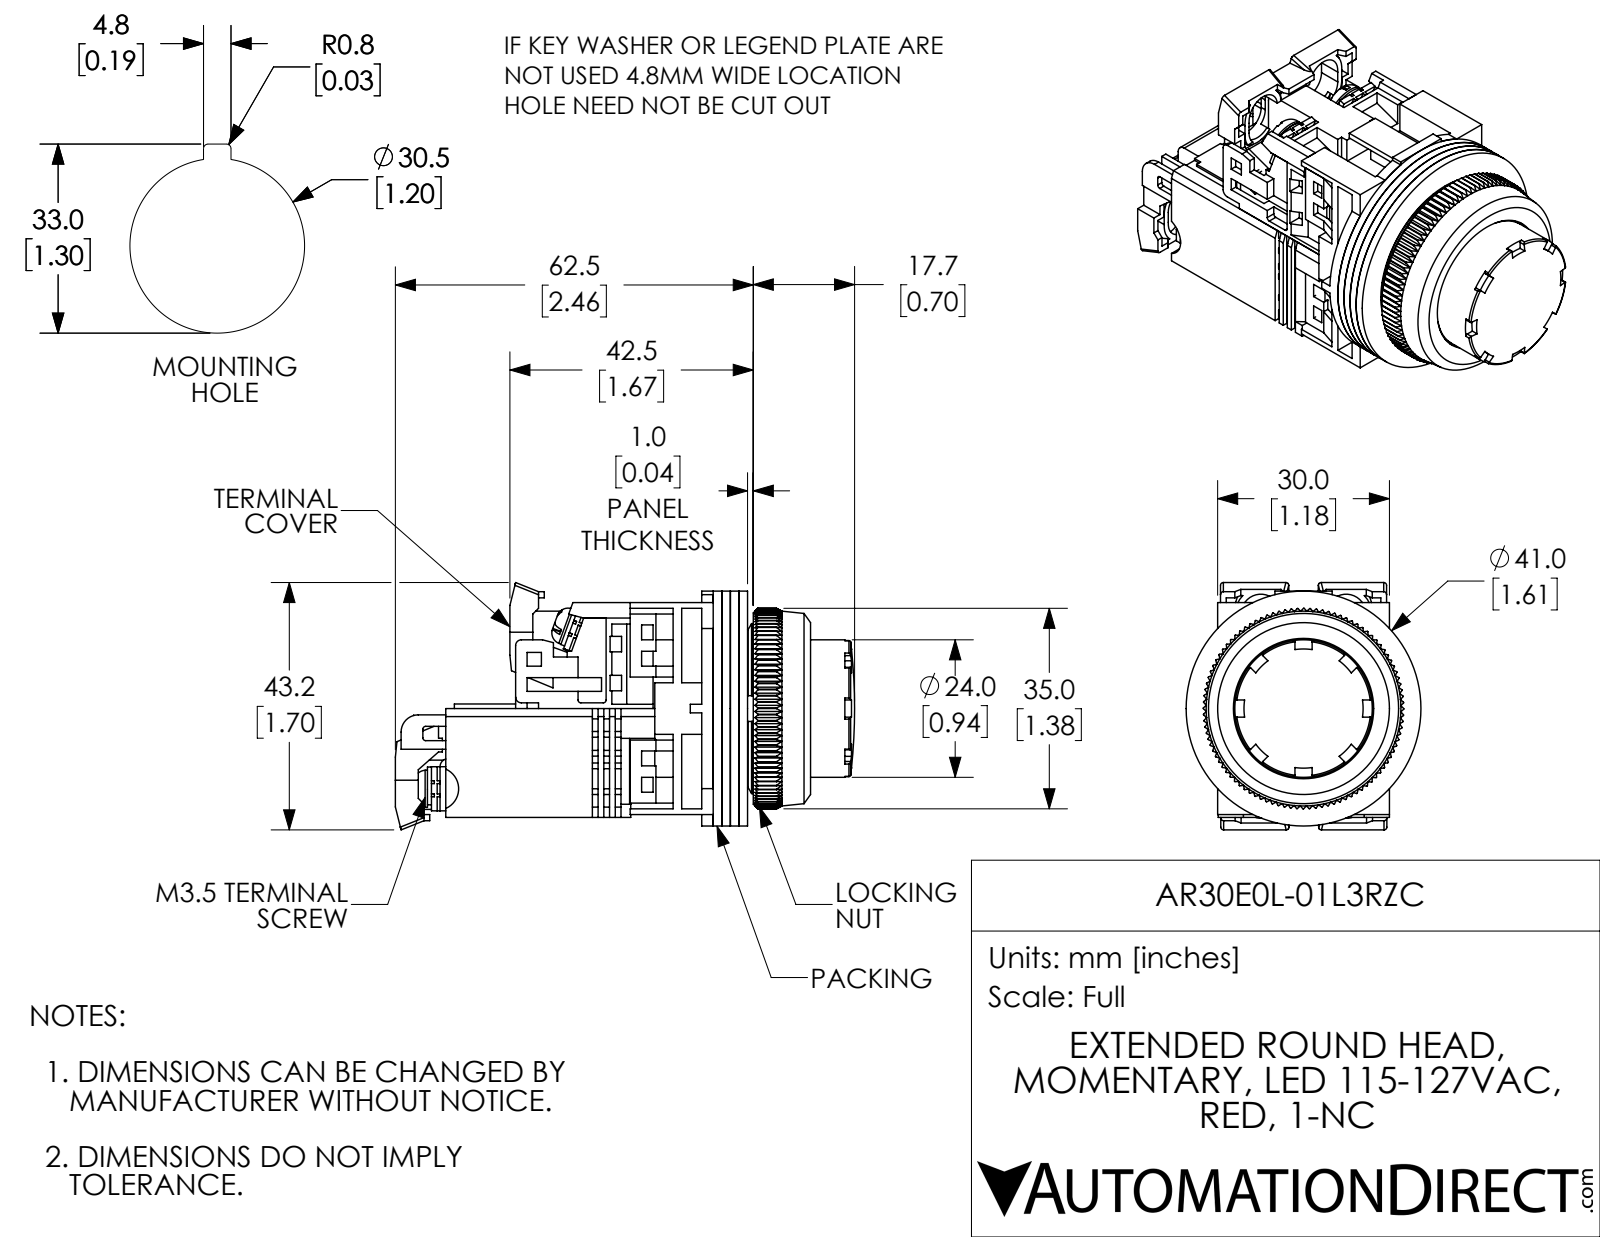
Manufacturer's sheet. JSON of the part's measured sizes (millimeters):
{"part_name": "AR30E0L-01L3RZC", "step_written_by": "SolidWorks 2017 (AUTOMOTIVE_DESIGN)", "units": "millimeters", "bodies": {"solids": 27, "faces": 1960, "planar": 1368, "cylindrical": 339, "other": 253}, "overall_size": [80.2, 43.2, 41], "volume_mm3": 47240, "surface_area_mm2": 41310, "round_holes": [[3.5, 6], [3.6, 4], [3, 3], [12, 1], [18, 1], [18.5, 1], [20, 1], [24, 1], [24.5, 1], [28.5, 1], [31.8, 1]], "round_bosses_or_shafts": [[6.6, 4], [3.5, 2], [41, 1], [30, 1], [22, 1], [19.7, 1], [14, 1]], "partial_cylinders_radius": [[1.5, 17], [0.3, 16], [0.5, 13], [3.5, 4], [4.5, 4], [1, 2], [3, 2], [0.4, 1]], "face_to_face_distances": [1.5, 3, 4.5, 19, 1, 0.5, 2, 36, 17.5, 1.2], "hole_center_spacings": [14.7, 0.5, 7.5, 7.6, 7.6, 14.8, 14.8, 15.4]}
